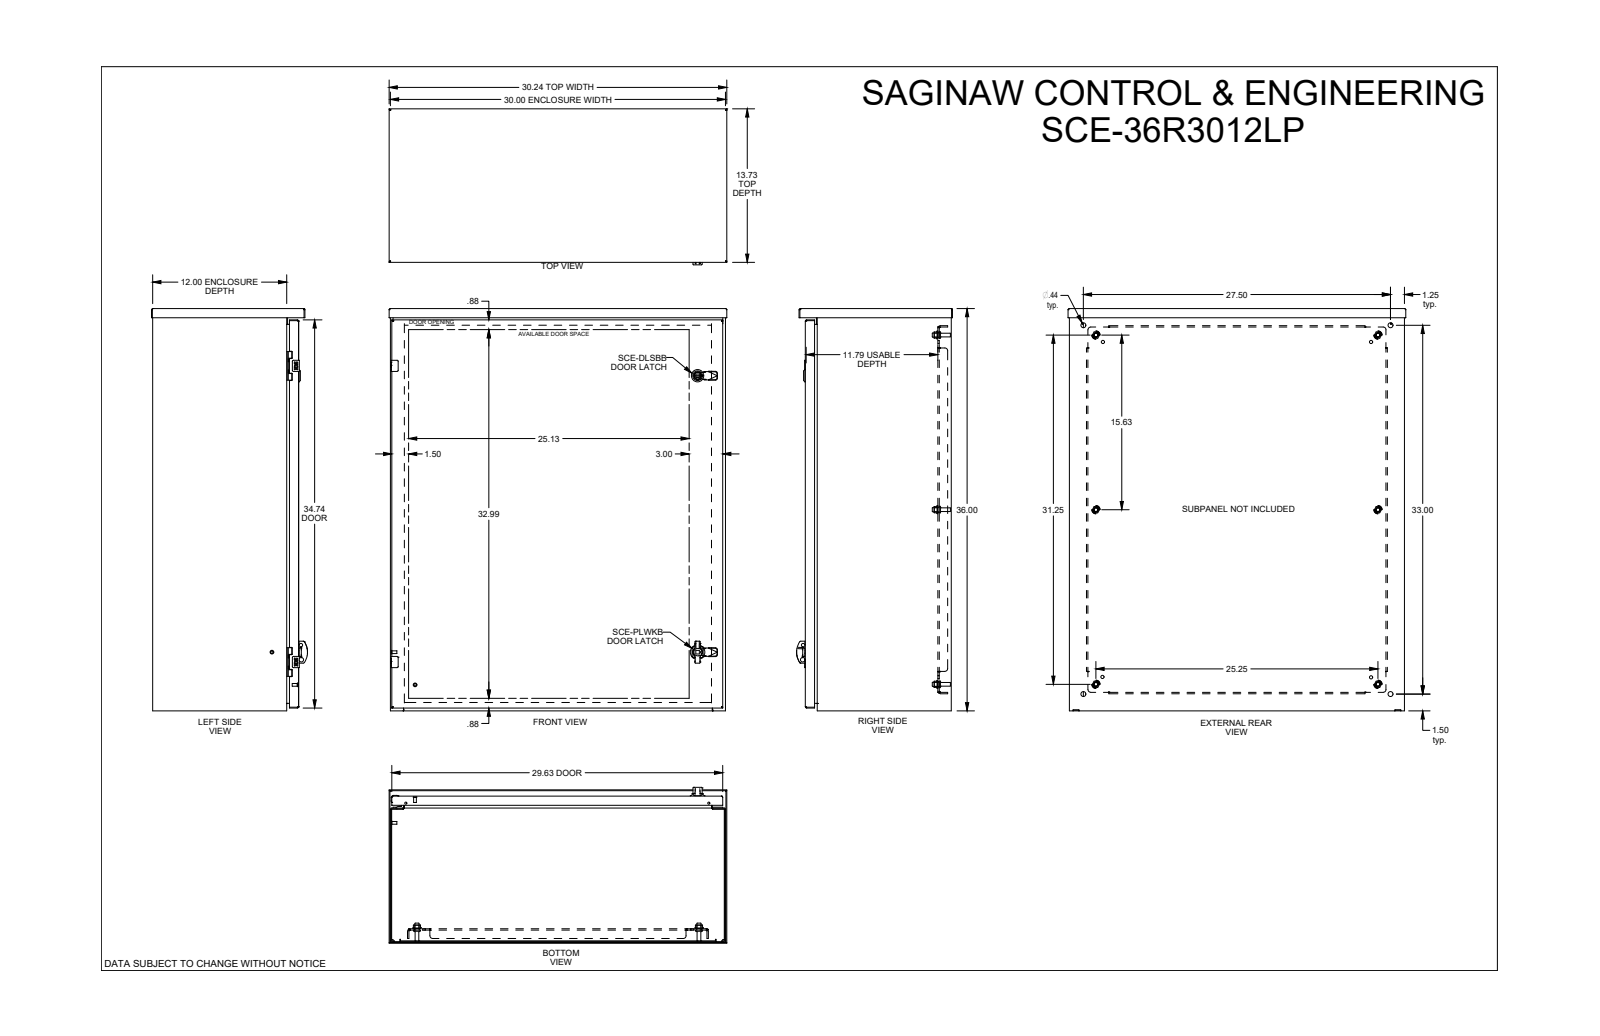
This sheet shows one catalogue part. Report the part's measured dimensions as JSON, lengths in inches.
{"part_name": "SCE-36R3012LP", "step_written_by": "SolidWorks 2019 (CONFIG_CONTROL_DESIGN)", "units": "inches", "bodies": {"solids": 0, "faces": 2607, "planar": 1214, "cylindrical": 875, "other": 518}, "overall_size": [36, 30.236, 13.957], "round_holes": [[0.367, 6], [0.5, 6], [0.172, 4], [0.205, 4], [0.244, 4], [0.266, 4], [0.281, 4], [0.375, 4], [0.438, 4], [0.04, 2], [0.156, 2], [0.188, 2]], "round_bosses_or_shafts": [[0.366, 6], [0.332, 6], [0.17, 6], [0.25, 4], [0.24, 4], [0.196, 3], [0.866, 2], [0.802, 2]], "partial_cylinders_radius": [[0.012, 60], [0.015, 54], [0.06, 45], [0.01, 38], [0.02, 24], [0.117, 21], [0.042, 19], [0.03, 15]], "face_to_face_distances": [0.075, 0.075, 12.918, 12.993, 13.068, 12.993, 0.125, 1, 1.125, 11.918], "hole_center_spacings": [26.5, 0.494, 0.875, 1.426, 15.625, 16.538, 26.389, 29.693]}
